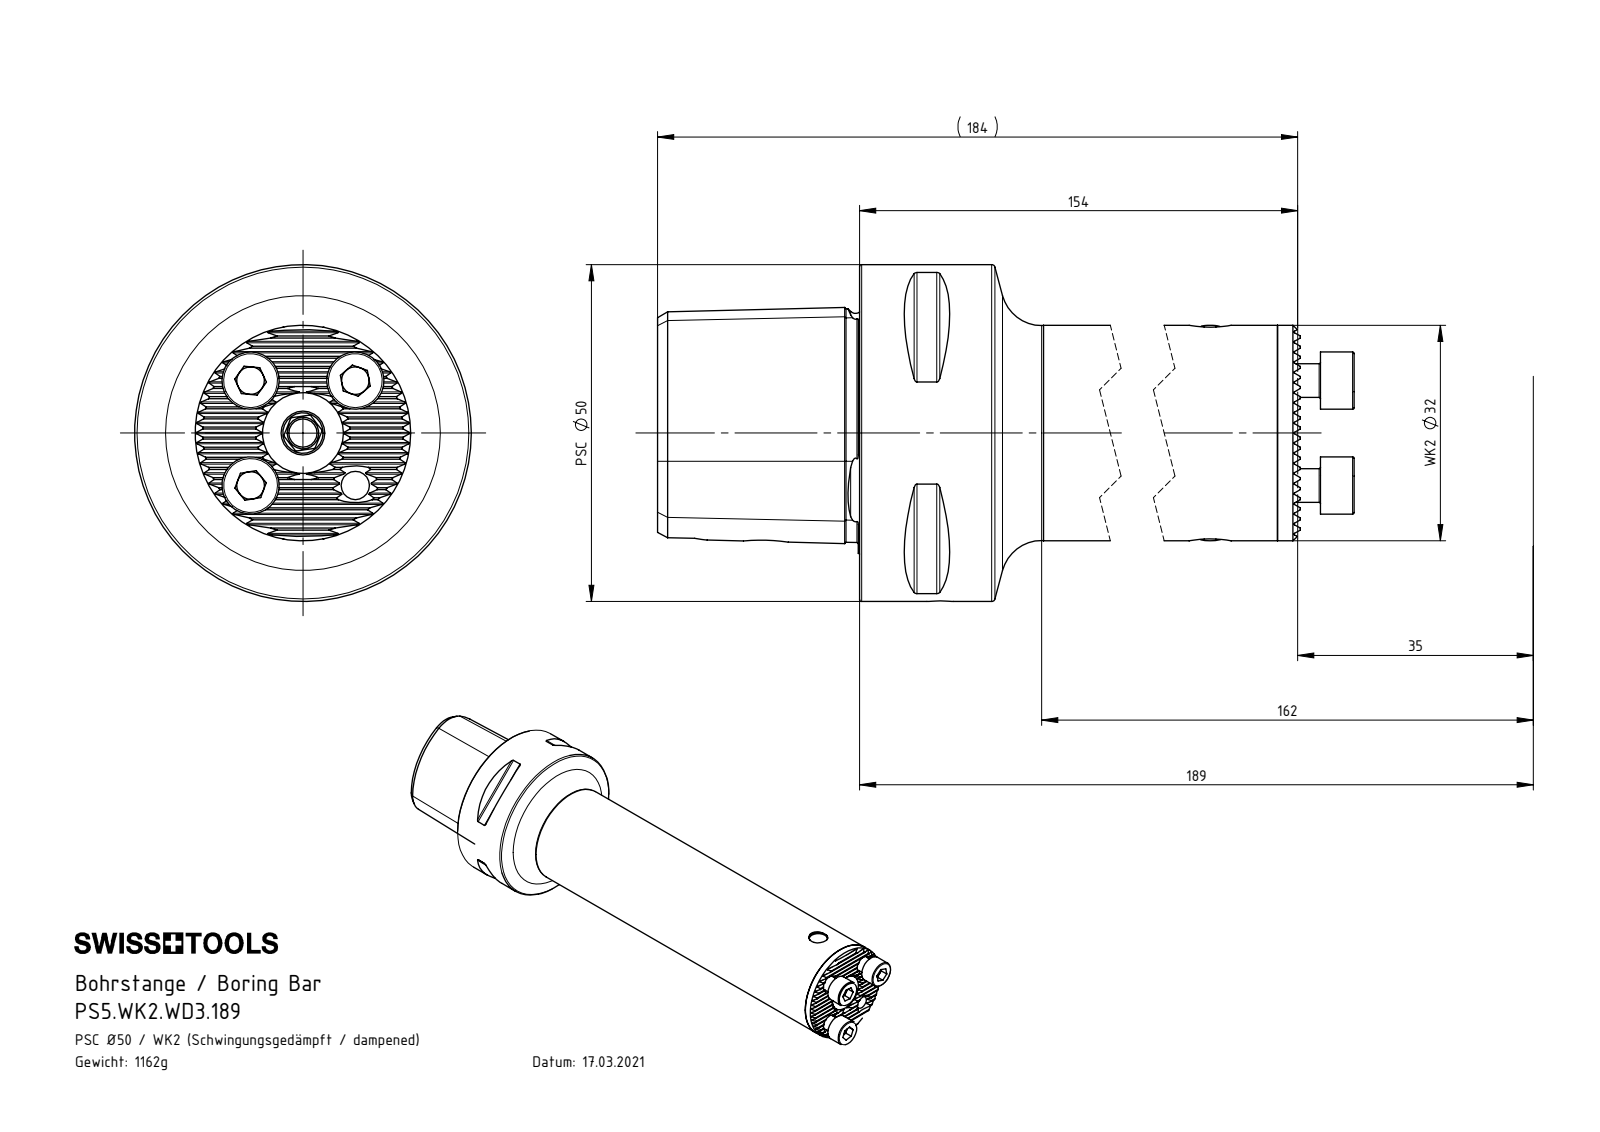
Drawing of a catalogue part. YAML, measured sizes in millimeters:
part_name: "DIN 3771 - 6x1; WD3-ER1.026.087_A; ISO 4762 - M5 x 14; DIN 3771 - 13x4 (+8 more)"
step_written_by: "SolidWorks 2017 (AUTOMOTIVE_DESIGN)"
units: millimeters
bodies: {solids: 15, faces: 393, planar: 216, cylindrical: 89, other: 88}
overall_size: [135.09, 32, 32]
volume: 61785
surface_area: 42244
round_holes:
  - {diameter: 4.2, count: 5}
  - {diameter: 6, count: 2}
  - {diameter: 6.8, count: 1}
  - {diameter: 7, count: 1}
  - {diameter: 7.4, count: 1}
  - {diameter: 8.2, count: 1}
  - {diameter: 8.5, count: 1}
  - {diameter: 12, count: 1}
  - {diameter: 14, count: 1}
  - {diameter: 21, count: 1}
round_bosses_or_shafts:
  - {diameter: 8.5, count: 3}
  - {diameter: 5, count: 3}
  - {diameter: 32, count: 1}
  - {diameter: 27.2, count: 1}
  - {diameter: 27, count: 1}
  - {diameter: 26.7, count: 1}
  - {diameter: 26, count: 1}
  - {diameter: 23.8, count: 1}
partial_cylinders:
  - {radius: 0.12, count: 21}
face_to_face_distances: [6, 93.4, 2.6, 1.3, 3.9, 99.4, 100.25, 0.85, 87.4, 94.25]
hole_center_spacings: [11, 15.56, 22.01]
